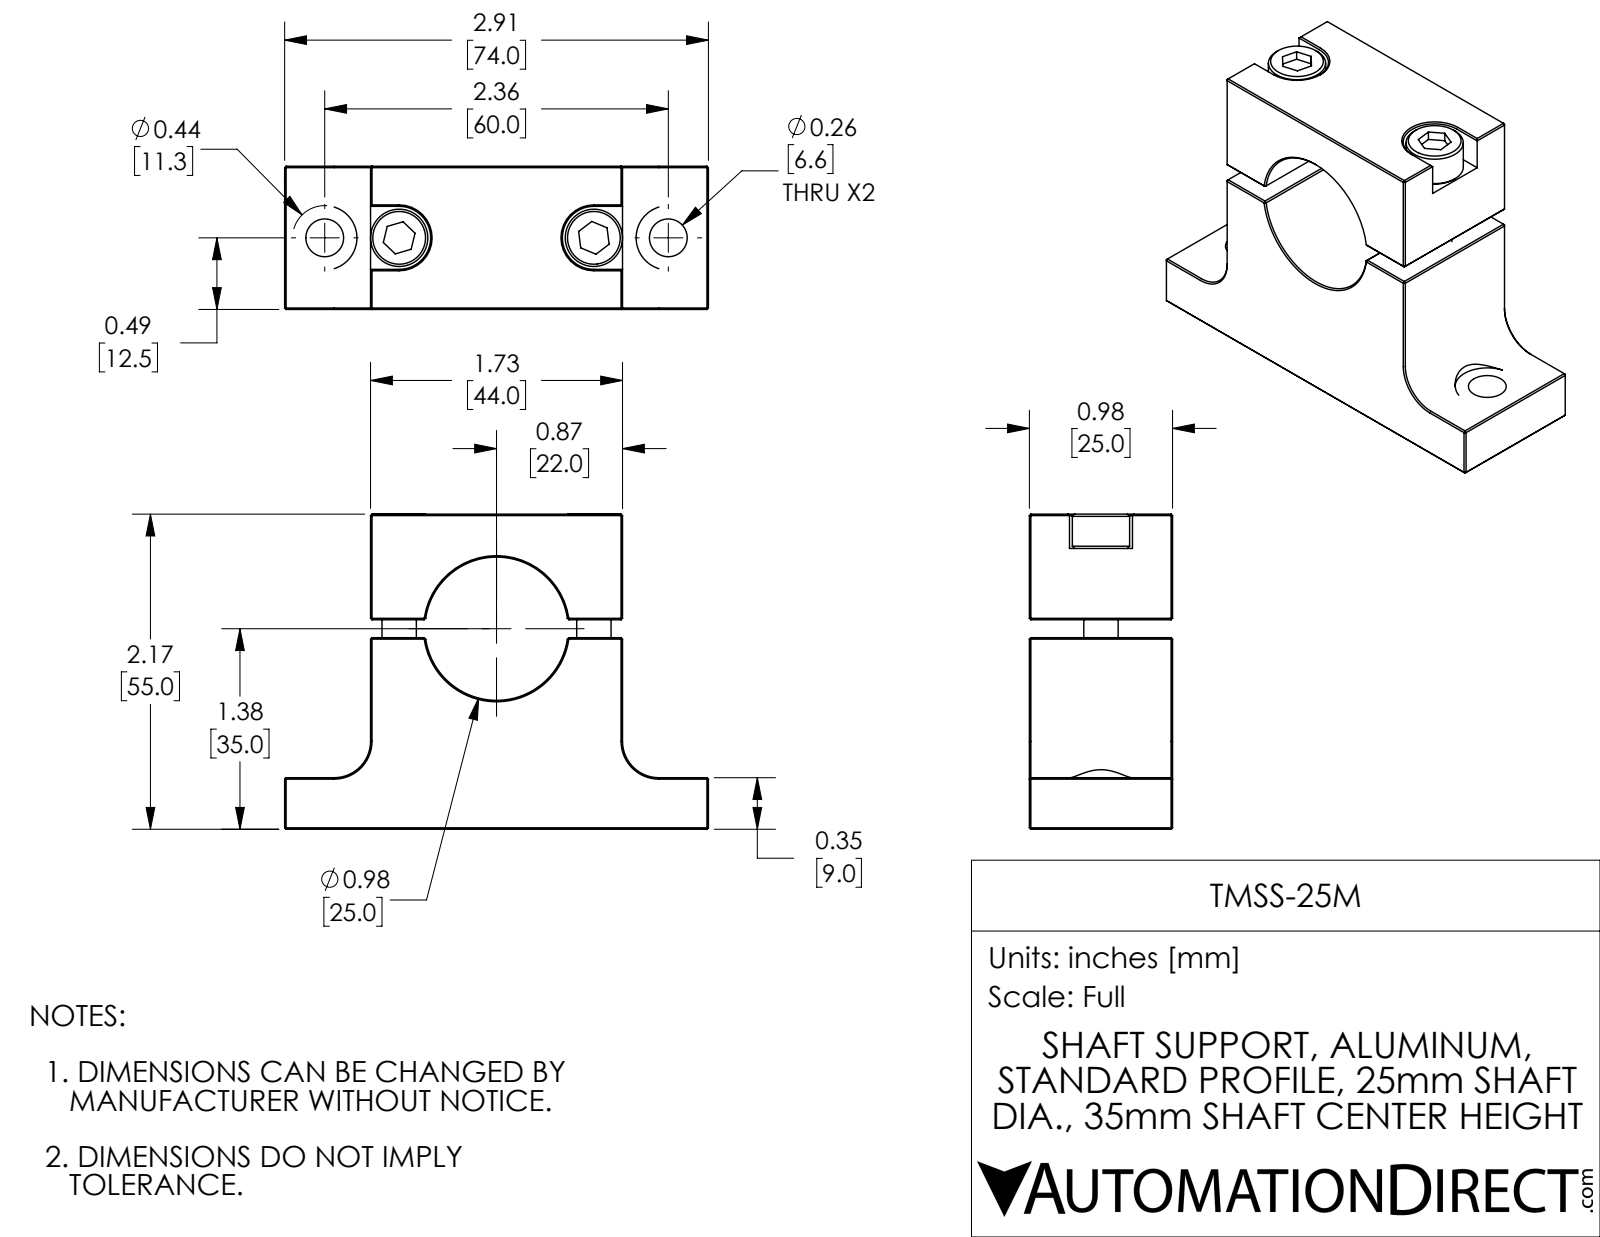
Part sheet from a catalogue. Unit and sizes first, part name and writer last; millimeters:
Units: millimetres
Overall size (bounding box): 74 × 55 × 25
Round holes (diameter × count): ⌀6.6 ×4, ⌀4.9 ×2, ⌀2.4 ×1, ⌀25 ×1
Round bosses / shafts (diameter × count): ⌀10 ×2, ⌀6 ×2
Partial cylindrical surfaces — rounded edges, fillets, slot ends (radius × count): R5.5 ×2, R5.6 ×2, R6.4 ×2
Main face-to-face distances: 25, 55, 44, 15, 59, 33.5, 21.6, 9, 24.4, 46
Hole centre spacings: 13, 17, 30, 47, 34, 60
Volume: 52 160 mm³ · Surface area: 16 520 mm²
Bodies: 4 solids, 177 faces (120 planar, 32 cylindrical, 25 other)
Part name (STEP PRODUCT): TMSS-25M
STEP written by: SolidWorks 2017 (AUTOMOTIVE_DESIGN)
